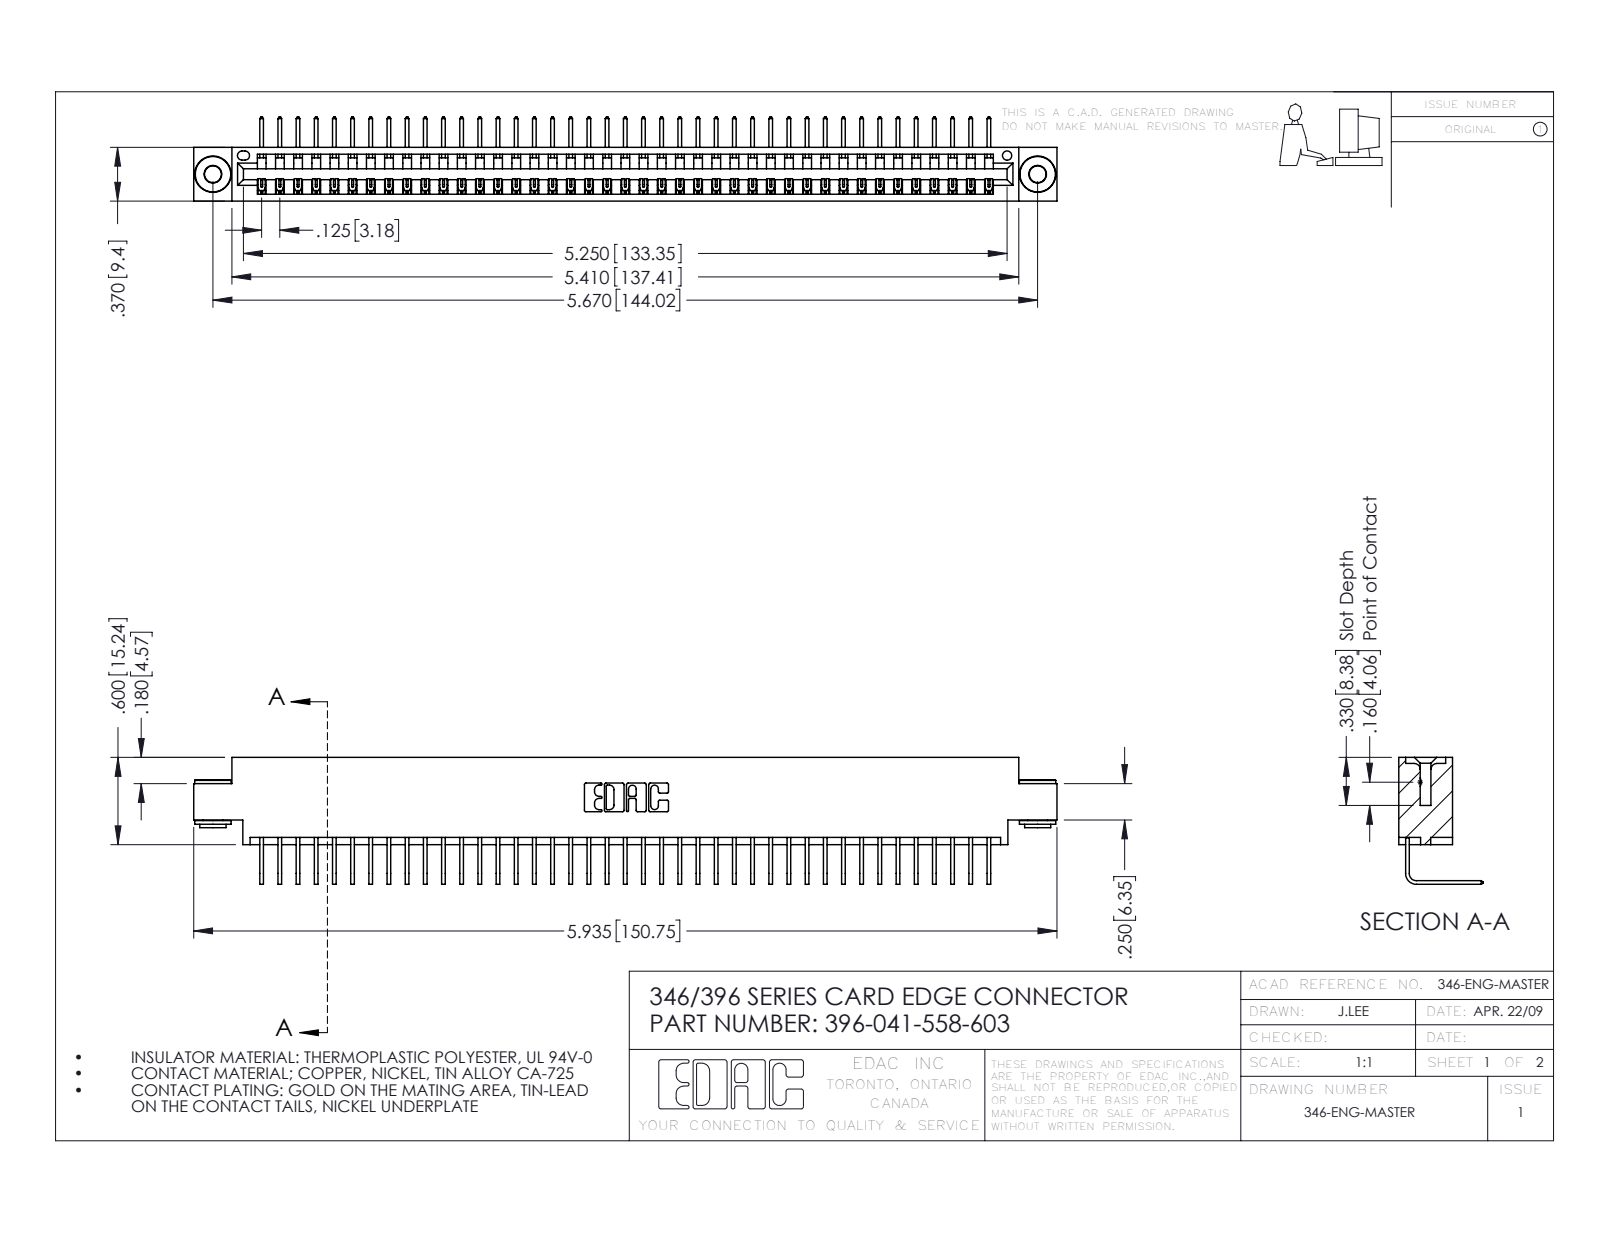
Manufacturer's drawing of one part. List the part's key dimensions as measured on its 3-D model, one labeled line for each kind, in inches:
Part name (STEP PRODUCT): 396-041-558-603; 345-292-001_558 Tail - 2; 345-250-002_345-250-002-102; 346 Part_0.170 Offset - 0.156 Dia-TH
STEP written by: SolidWorks 2016 (CONFIG_CONTROL_DESIGN)
Units: inches
Bodies: 44 solids, 2624 faces (1812 planar, 804 cylindrical, 8 other)
Overall size (bounding box): 5.935 × 0.873 × 0.58
Volume: 0.88 in³ · Surface area: 29.78 in²
Round holes (diameter × count): ⌀0.116 ×2, ⌀0.156 ×2, ⌀0.064 ×1
Round bosses / shafts (diameter × count): ⌀0.25 ×2, ⌀0.18 ×2, ⌀0.136 ×2
Partial cylindrical surfaces — rounded edges, fillets, slot ends (radius × count): R0.006 ×82, R0.01 ×22, R0.007 ×6, R0.031 ×6, R0.026 ×3, R0.031 ×2, R0.04 ×2, R0.014 ×1
Main face-to-face distances: 0.322, 0.048, 0.37, 0.25, 0.025, 0.298, 0.072, 0.148, 0.222, 0.1
Hole centre spacings: 0.246, 5.461, 5.67
